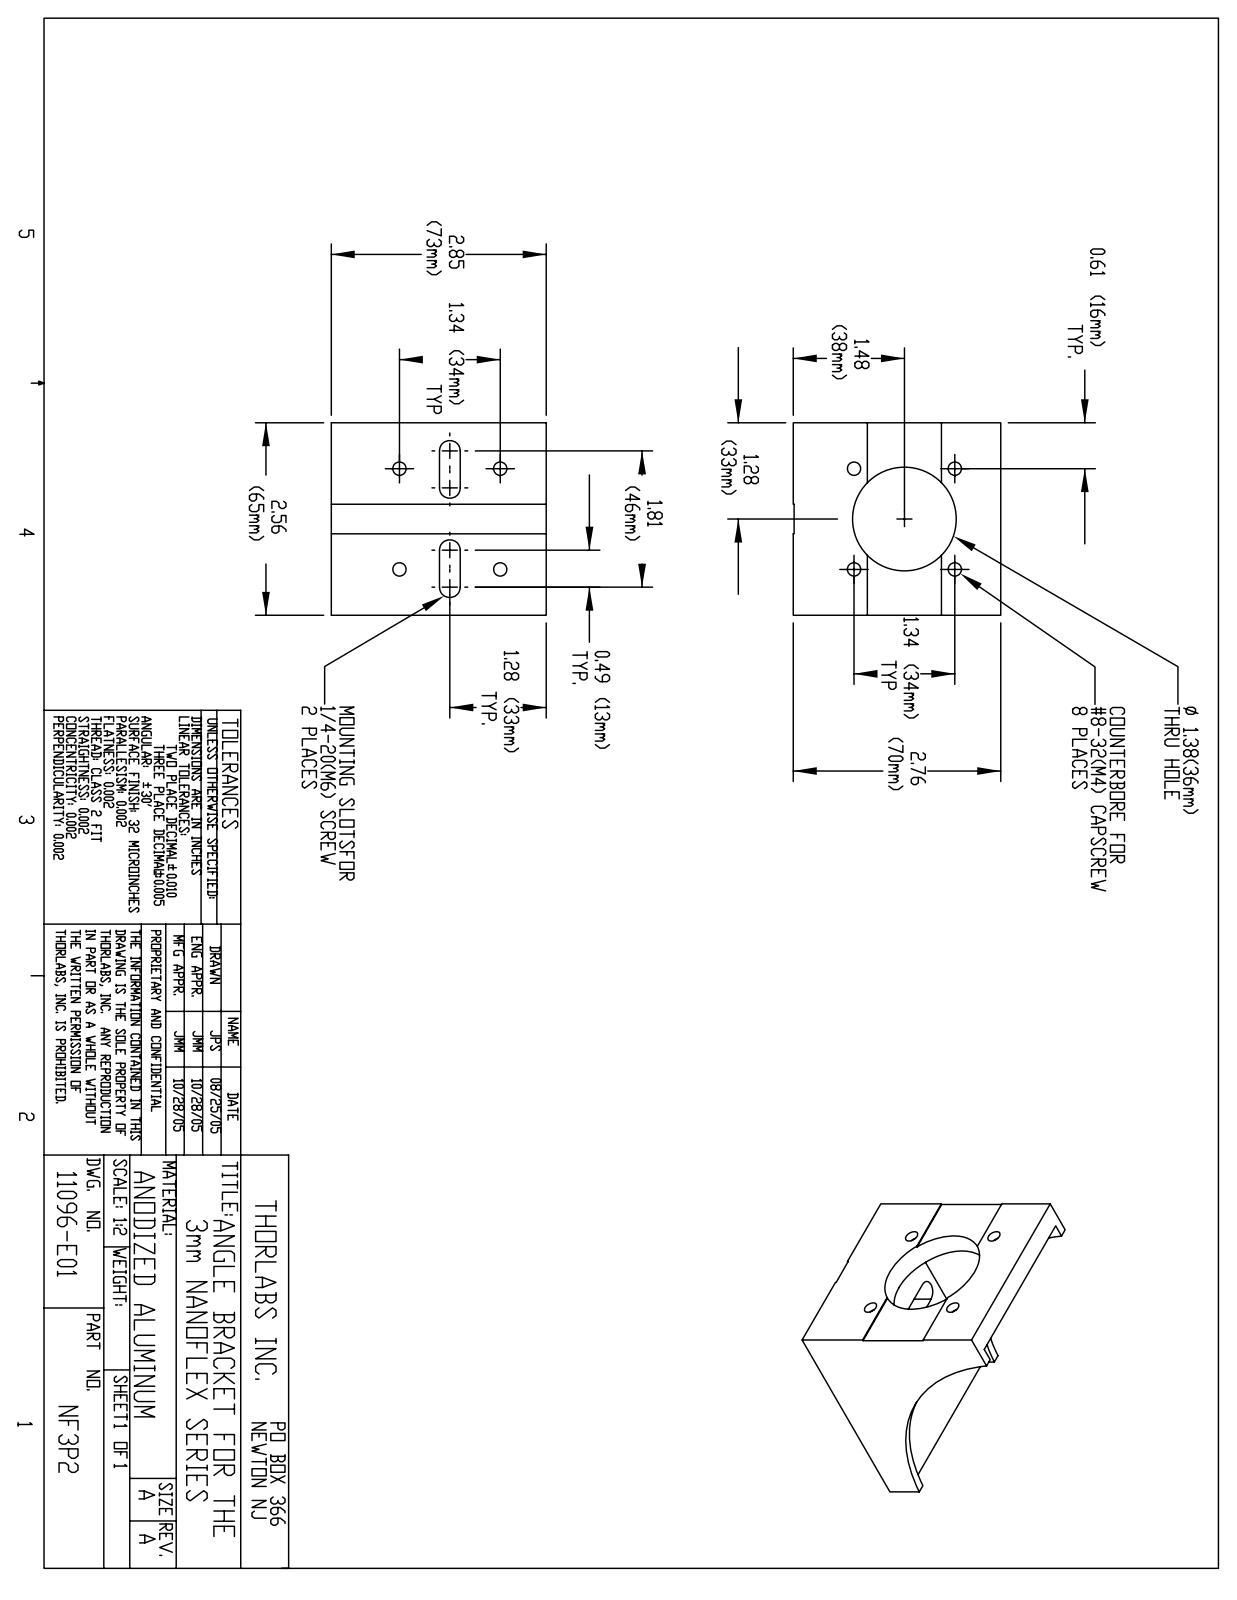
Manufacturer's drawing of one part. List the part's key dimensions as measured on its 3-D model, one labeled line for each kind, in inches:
Part name (STEP PRODUCT): 11096-E0W
STEP written by: SolidWorks 2007 (AUTOMOTIVE_DESIGN)
Units: inches
Bodies: 0 solids, 79 faces (33 planar, 46 cylindrical, 0 other)
Overall size (bounding box): 2.854 × 2.756 × 2.559
Round holes (diameter × count): ⌀0.177 ×8, ⌀0.315 ×8, ⌀1.378 ×1
Partial cylindrical surfaces — rounded edges, fillets, slot ends (radius × count): R0.138 ×4, R0.492 ×4, R2.559 ×1
Main face-to-face distances: 0.295, 2.559, 0.118, 2.441, 0.283, 2.323, 2.461, 2.744, 2.756, 2.843
Hole centre spacings: 1.339, 0.946, 1.893
